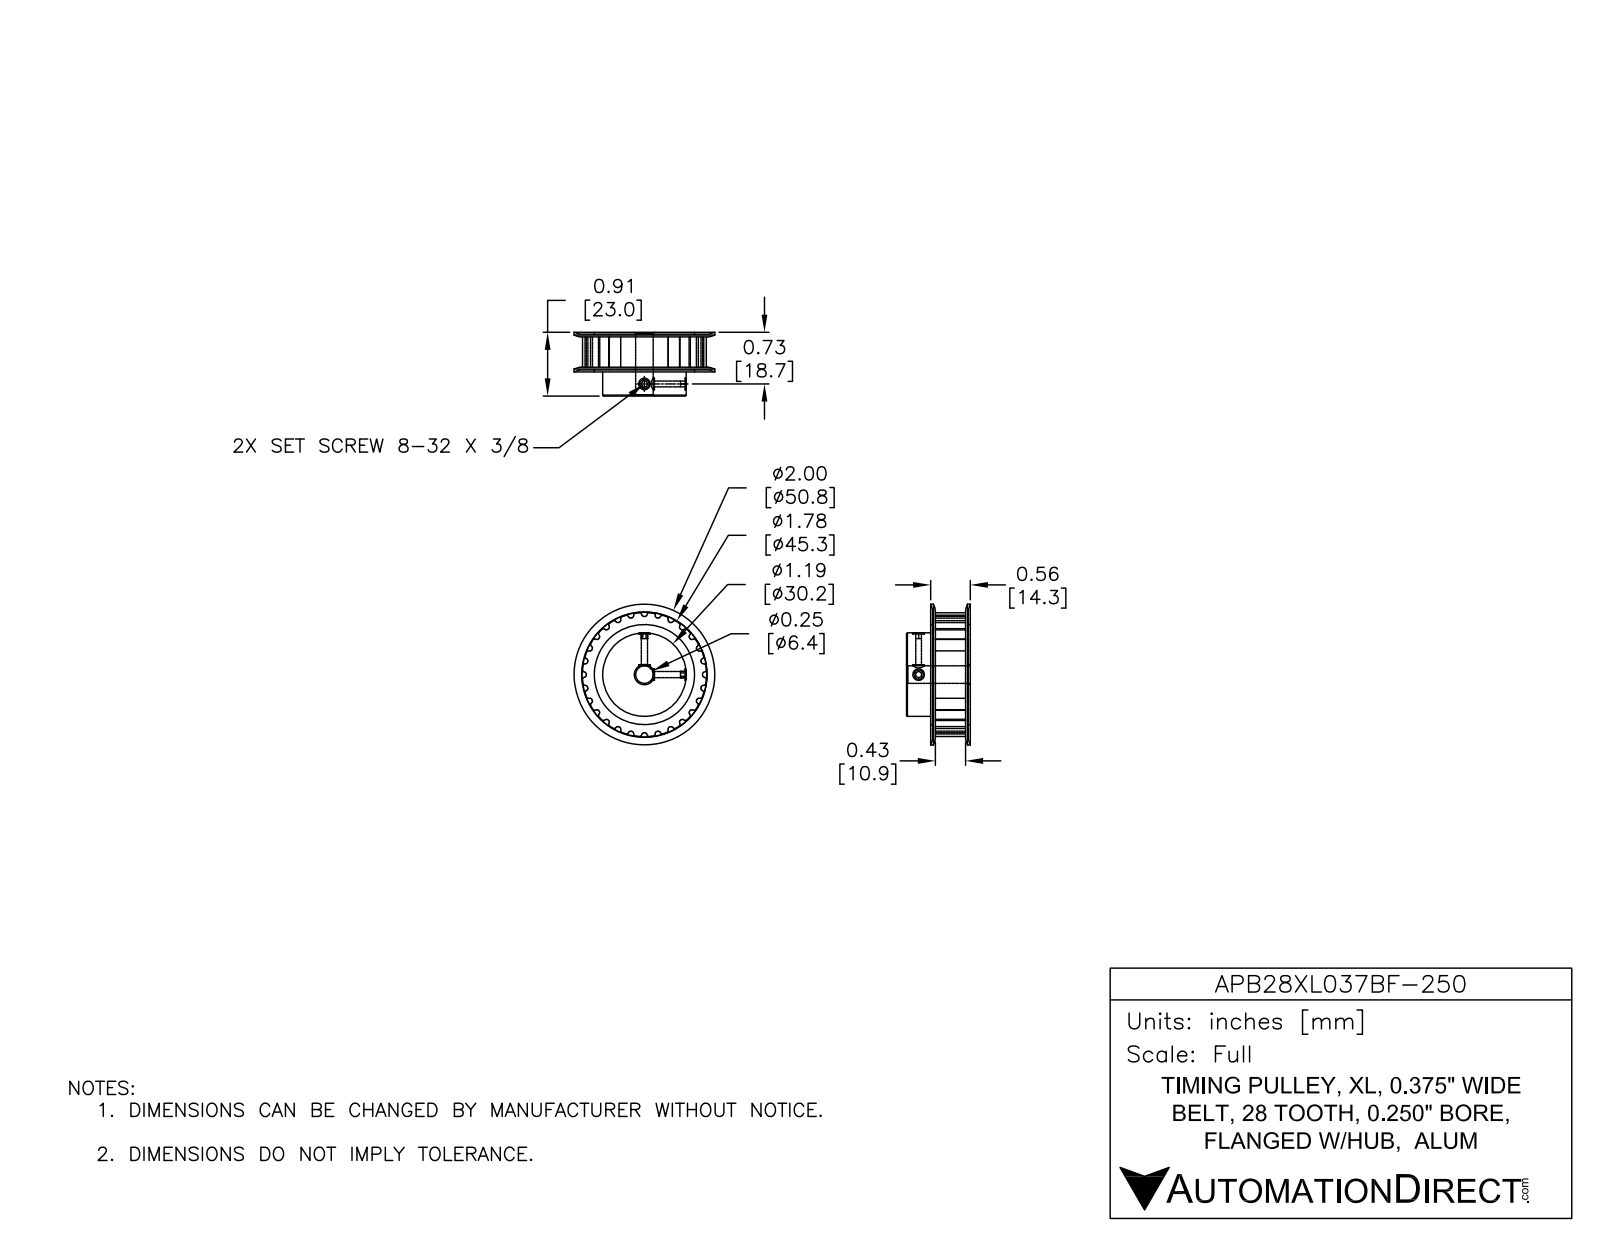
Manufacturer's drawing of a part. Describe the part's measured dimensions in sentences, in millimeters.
The part is named "APB28XL037BF-250". Its 3-D file was written by "SolidWorks 2014 (AUTOMOTIVE_DESIGN)". It is 1 solid with 281 faces: 90 planar, 169 cylindrical and 22 other. Overall it measures 50.8 by 50.8 by 23.01 millimeters. Its volume is 26 364 cubic millimeters and its surface area 8 865 square millimeters. Round holes: 2 of diameter 2.23, 1 of diameter 6.35. Round bosses or shafts: 1 of diameter 30.18. Partial cylindrical surfaces (rounded edges, fillets, slot ends): 112 of radius 0.38, 1 of radius 20.99. The main face-to-face distances are 12.57, 0.83, 13.4, 23.01, 22.18, 9.61, 44.78, 16.6, 11.74, 10.44.
